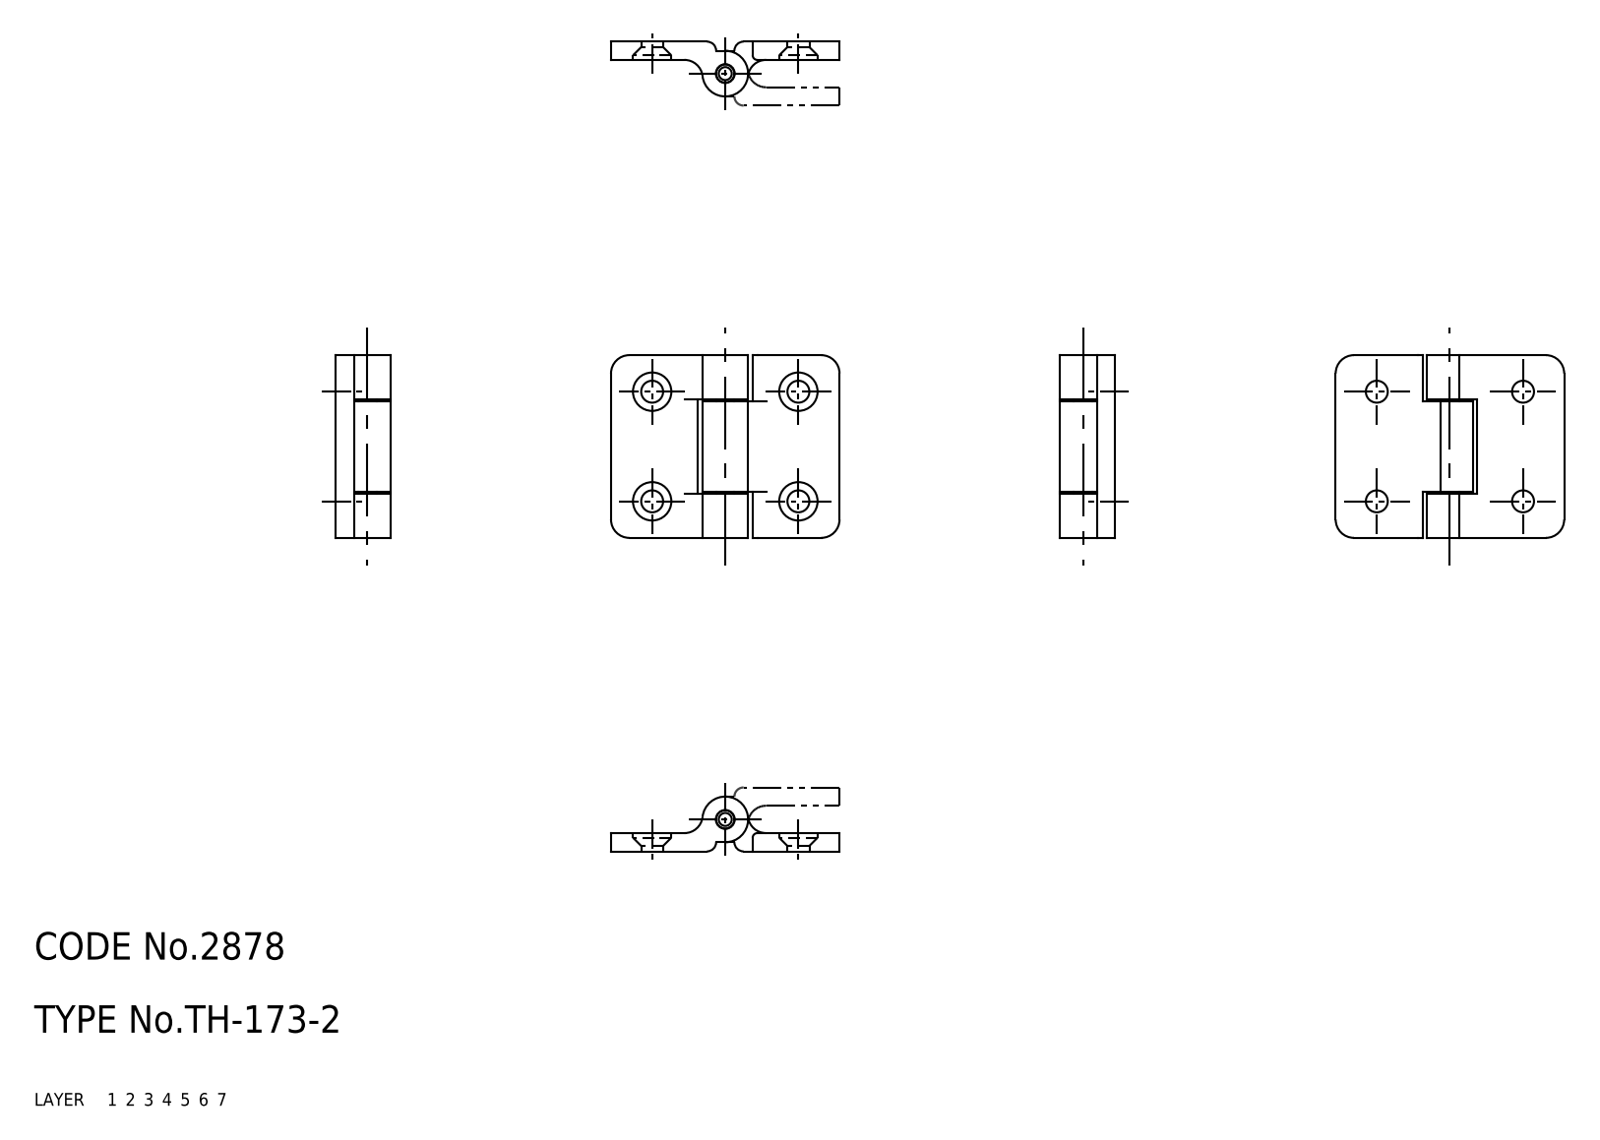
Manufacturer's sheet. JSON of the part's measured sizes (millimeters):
{"part_name": "shaft; hinge piece_A; hinge piece_B; TH_173_2", "step_written_by": "SolidWorks 2015 (AUTOMOTIVE_DESIGN)", "units": "millimeters", "bodies": {"solids": 3, "faces": 75, "planar": 22, "cylindrical": 45, "other": 8}, "overall_size": [25, 20, 6], "volume_mm3": 1157, "surface_area_mm2": 1675, "round_holes": [[2.4, 4], [4.2, 4], [2, 1]], "round_bosses_or_shafts": [[5, 1]], "partial_cylinders_radius": [[2, 6], [0.5, 2], [1, 2]], "face_to_face_distances": [2, 20, 4.8, 15.2, 5, 15, 10.2, 9.5, 15.5, 25], "hole_center_spacings": [12, 16, 20]}
